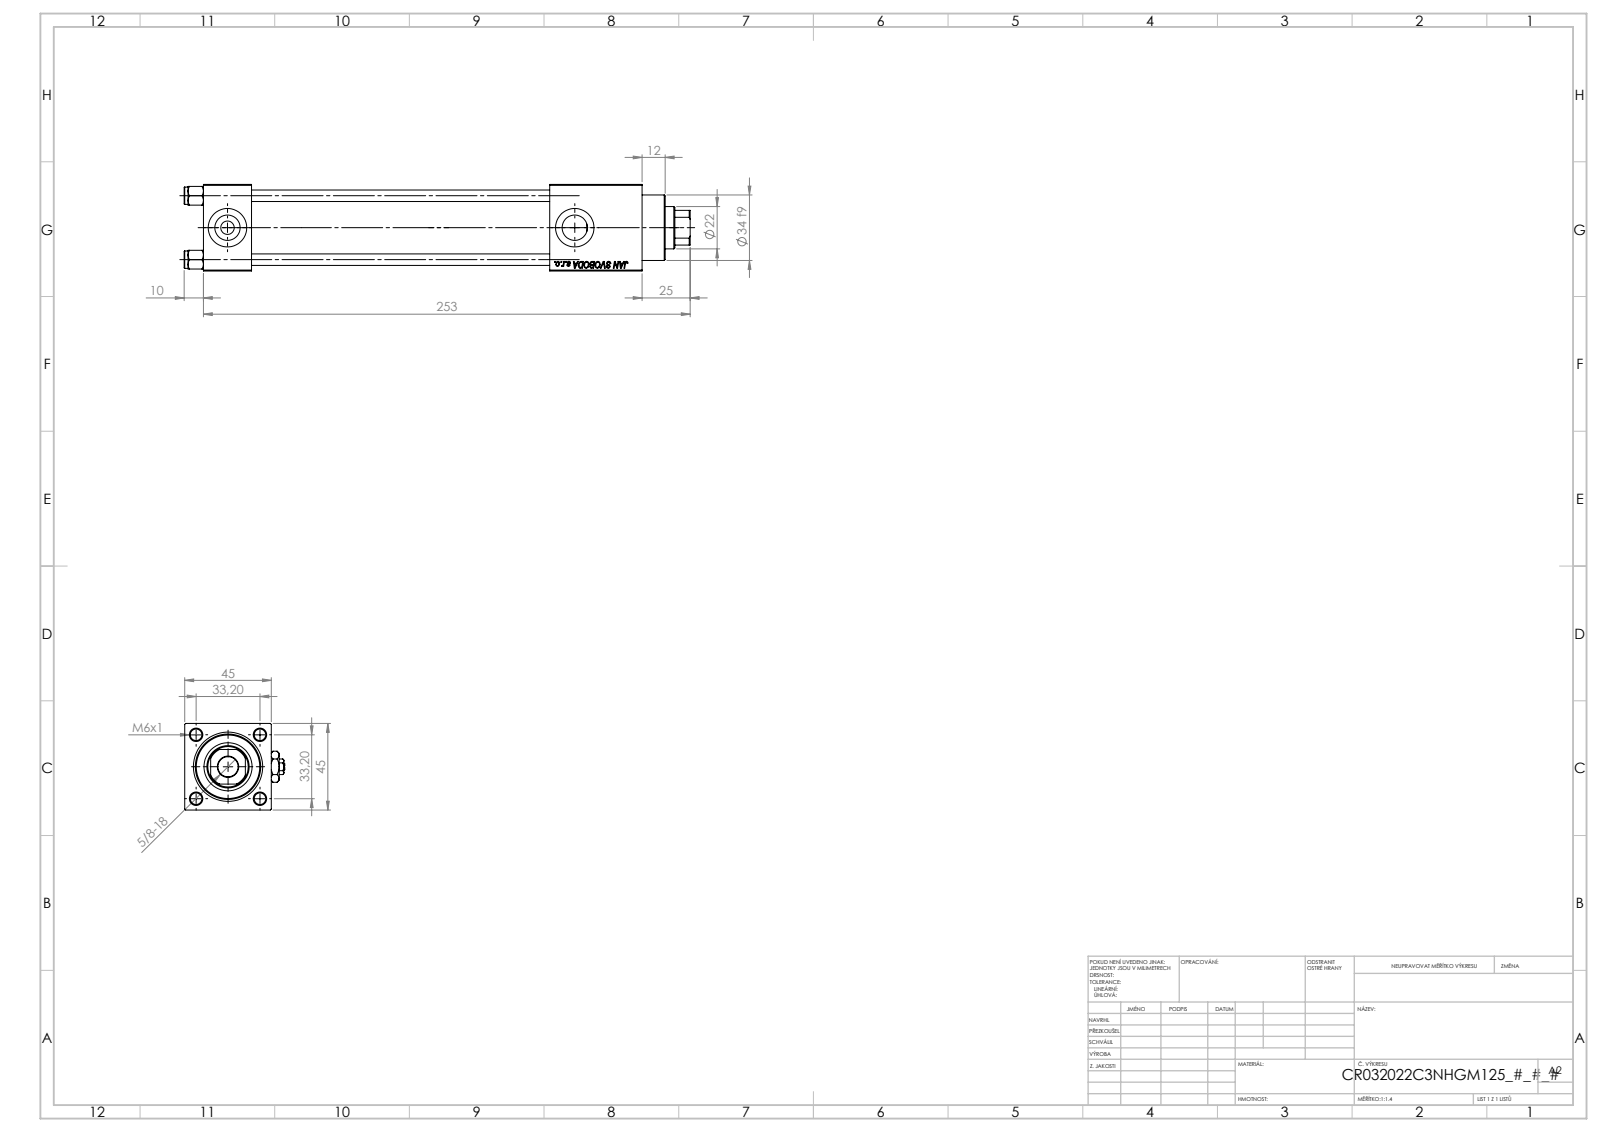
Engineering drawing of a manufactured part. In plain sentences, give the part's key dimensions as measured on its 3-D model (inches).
The part is named "V215CR_C_Body; NUT_M5_C; V215_VC_A; Zatka_pro_OIL_PORT (+2 more)". Its 3-D file was written by "SolidWorks 2019 (CONFIG_CONTROL_DESIGN)". It is 13 solids with 1248 faces: 572 planar, 98 cylindrical and 578 other. Overall it measures 10.354 by 2.047 by 1.772 inches. Its volume is 17.99 cubic inches and its surface area 172.7 square inches. Round holes: 4 of diameter 0.236, 2 of diameter 0.276, 2 of diameter 0.518, 2 of diameter 0.787, 1 of diameter 0.413, 1 of diameter 0.866, 1 of diameter 0.945, 1 of diameter 0.984, 1 of diameter 1.26, 1 of diameter 1.299. Round bosses or shafts: 4 of diameter 0.354, 1 of diameter 1.496, 1 of diameter 1.339. Partial cylindrical surfaces (rounded edges, fillets, slot ends): 1 of radius 0.413. The main face-to-face distances are 1.772, 0.984, 8.976, 7.087, 6.102, 7.992, 1.764, 1.89, 7.846, 6.862. The hole center spacings are 0.924, 1.307, 1.848, 7.106.
